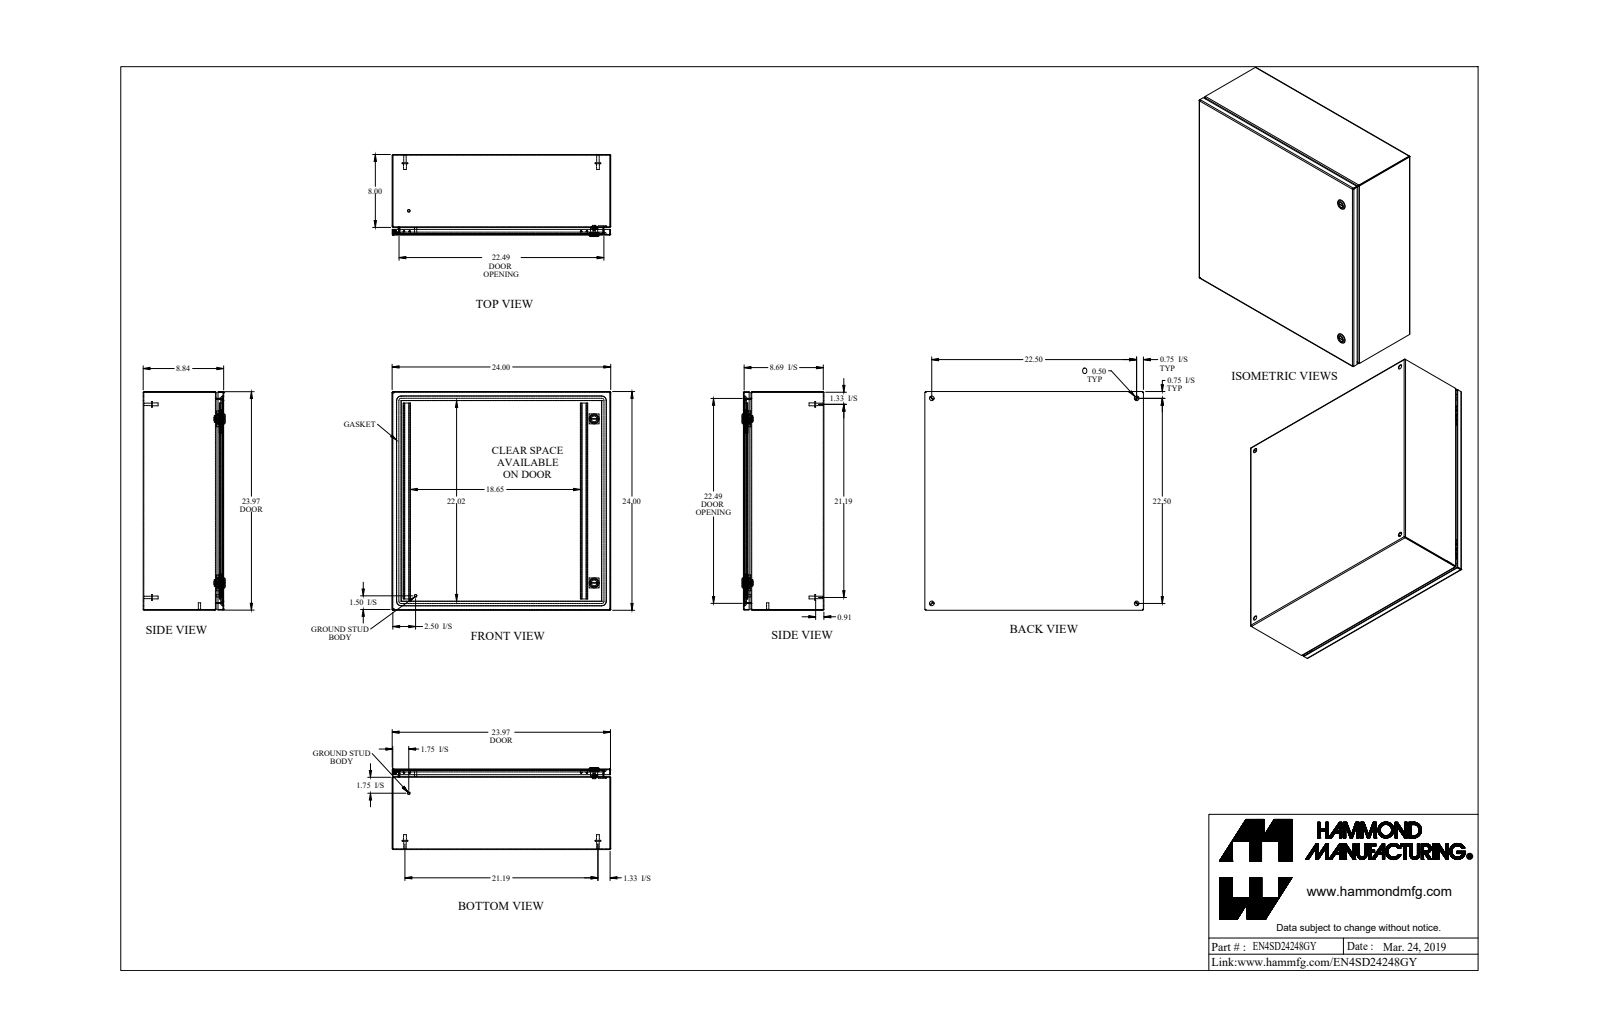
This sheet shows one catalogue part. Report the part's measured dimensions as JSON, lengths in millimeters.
{"part_name": "EN4SD24248GY_Default", "step_written_by": "SolidWorks 2019 (CONFIG_CONTROL_DESIGN)", "units": "millimeters", "bodies": {"solids": 27, "faces": 783, "planar": 386, "cylindrical": 257, "other": 140}, "overall_size": [609.6, 609.6, 228.5], "volume_mm3": 2686000, "surface_area_mm2": 2961000, "round_holes": [[12.7, 4], [5.9, 2], [15.9, 2], [19.9, 2], [4.4, 1], [6.1, 1], [6.1, 1]], "round_bosses_or_shafts": [[15.9, 4], [8, 4], [6.9, 4], [27.9, 2], [13.3, 2], [7.1, 2], [6.4, 2], [11.6, 1]], "partial_cylinders_radius": [[0.9, 20], [2.7, 20], [1.1, 12], [2.1, 12], [9.7, 12], [482.7, 8], [0.2, 4], [1.6, 4]], "face_to_face_distances": [1.8, 222.6, 607.8, 220.8, 224.5, 605.9, 609.6, 21.3, 201.4, 19.1], "hole_center_spacings": [571.5, 808.2, 63.3, 63.3, 457.2, 515, 515.1, 547.2]}
